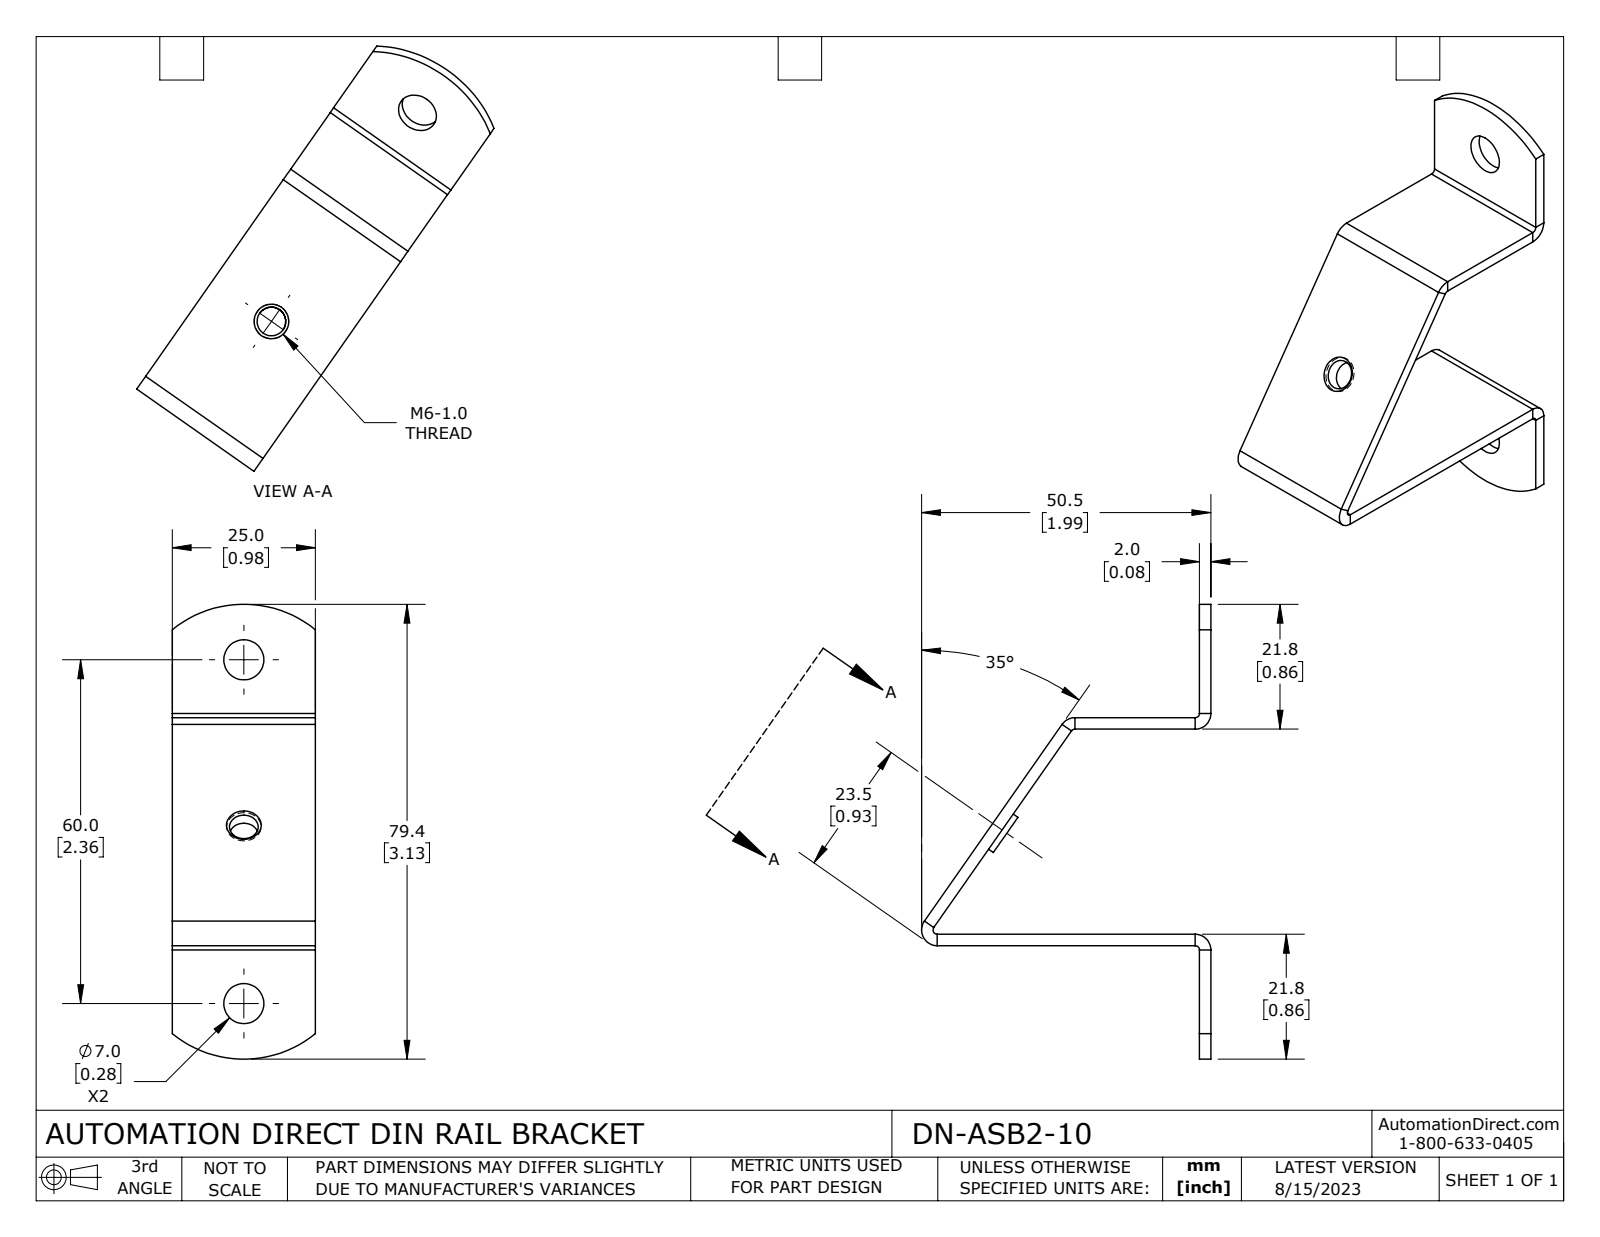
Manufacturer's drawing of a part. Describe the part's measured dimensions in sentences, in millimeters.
The part is named "DN-ASB2-10". Its 3-D file was written by "SolidWorks 2021 (CONFIG_CONTROL_DESIGN)". It is 1 solid with 50 faces: 29 planar, 19 cylindrical and 2 other. Overall it measures 79.4 by 50.52 by 25 millimeters. Its volume is 7 538 cubic millimeters and its surface area 8 371 square millimeters. Round holes: 2 of diameter 7, 1 of diameter 5. Round bosses or shafts: 1 of diameter 7.5. Partial cylindrical surfaces (rounded edges, fillets, slot ends): 4 of radius 0.74, 4 of radius 2.74, 2 of radius 19.78. The main face-to-face distances are 2, 37.8, 39.8, 35.8, 25, 1.01, 3.01. The hole center spacings are 60.
